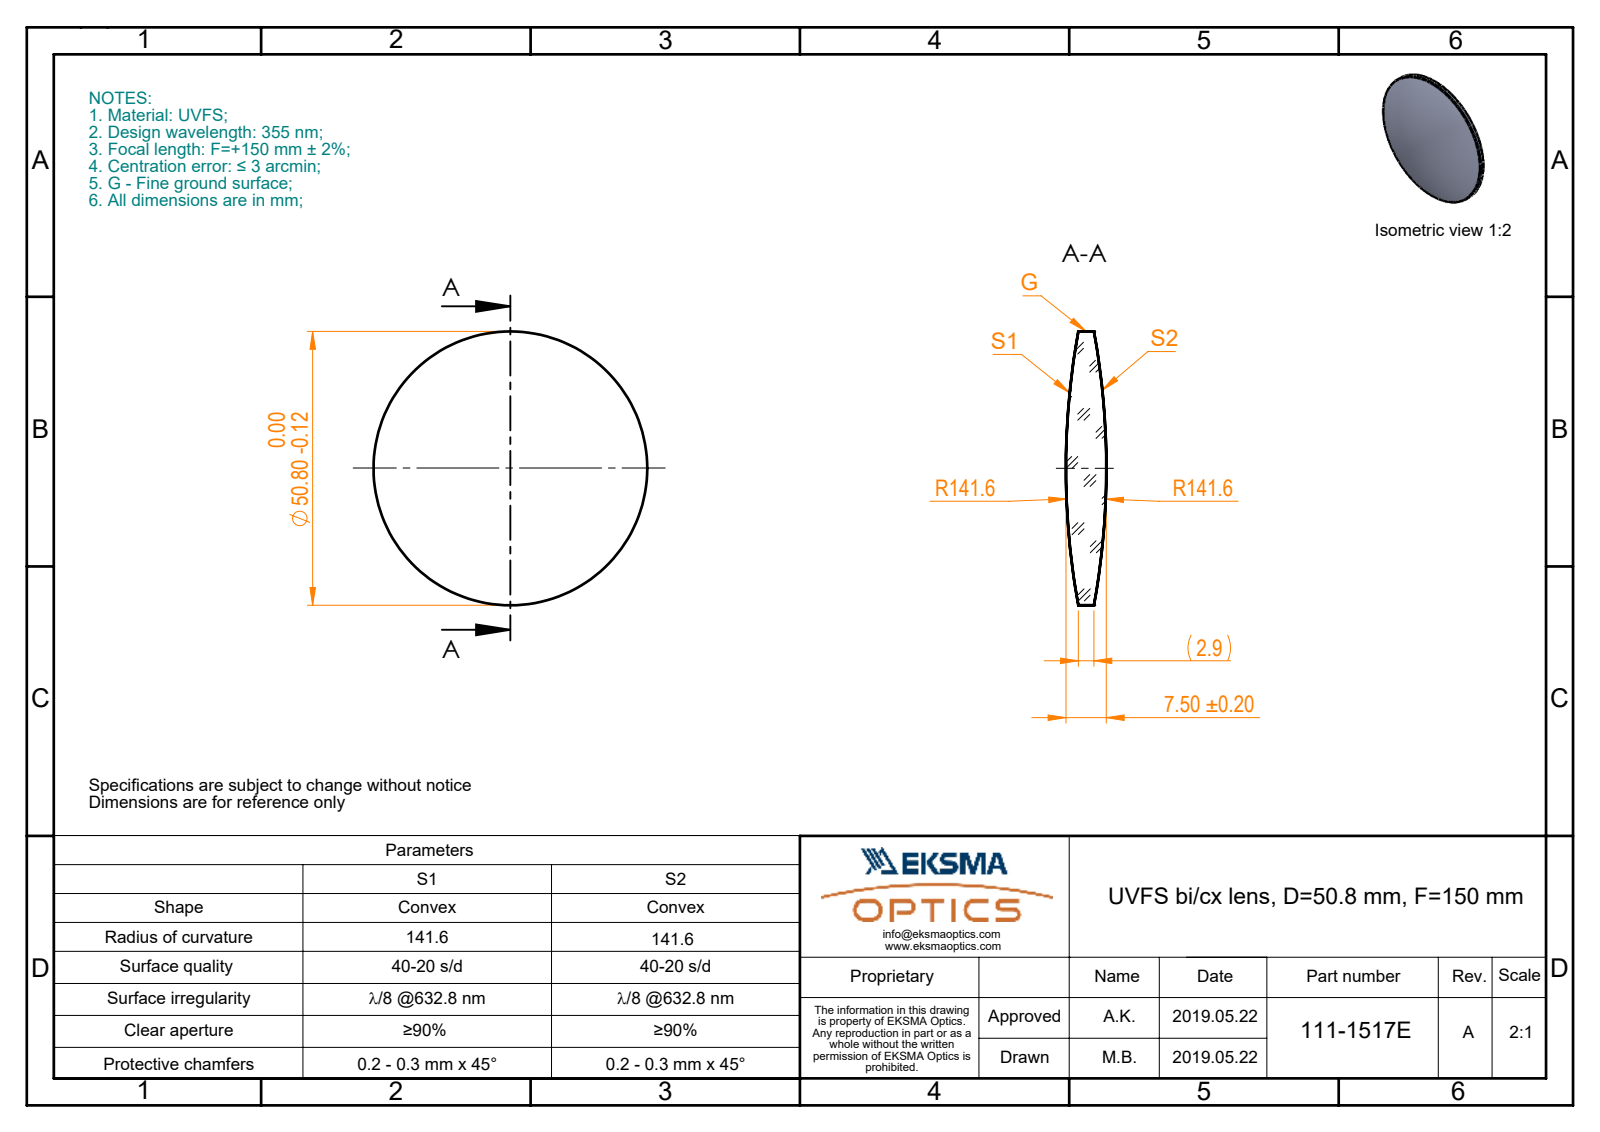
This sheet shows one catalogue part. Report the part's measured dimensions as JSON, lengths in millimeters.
{"part_name": "111-1517E UVFS bi-cx 50.8 F150", "step_written_by": "SolidWorks 2017 (CONFIG_CONTROL_DESIGN)", "units": "millimeters", "bodies": {"solids": 1, "faces": 6, "planar": 0, "cylindrical": 2, "other": 4}, "overall_size": [50.8, 50.8, 7.5], "volume_mm3": 10559, "surface_area_mm2": 4551, "round_bosses_or_shafts": [[50.8, 1]]}
